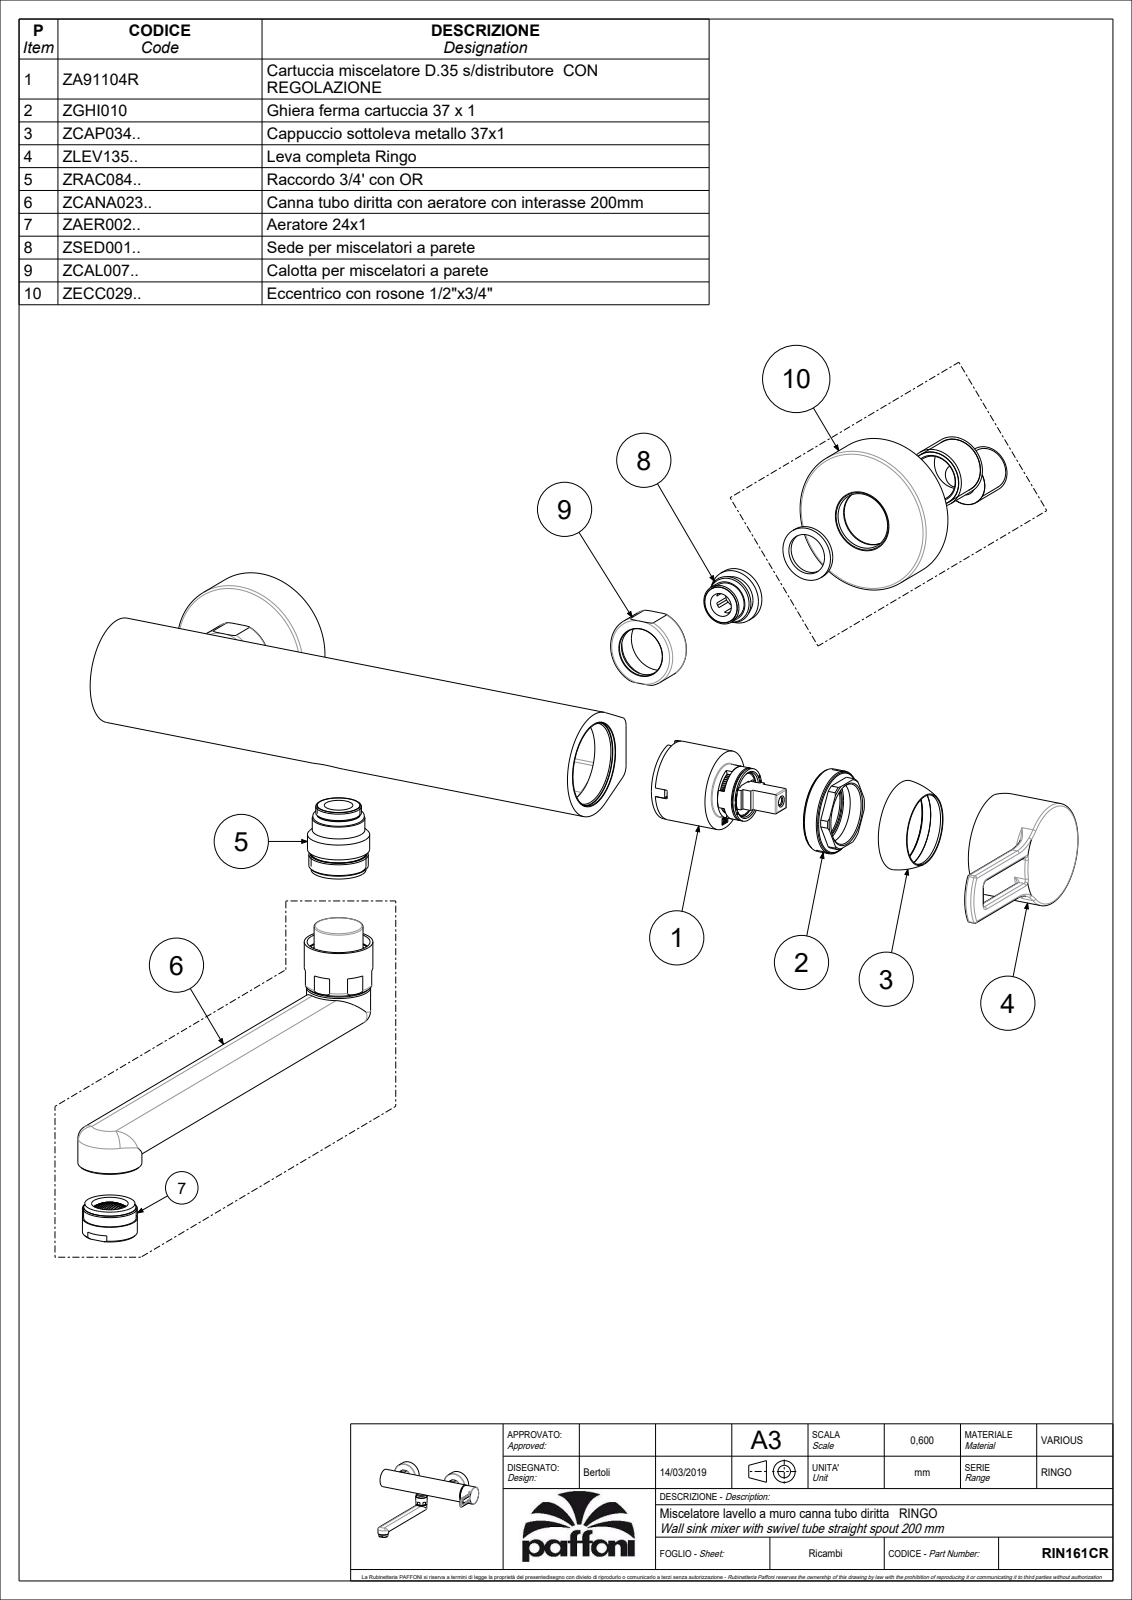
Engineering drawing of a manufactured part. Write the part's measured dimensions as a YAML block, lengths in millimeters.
part_name: "RIN161CR"
step_written_by: "CREO PARAMETRIC BY PTC INC, 2020044 (CONFIG_CONTROL_DESIGN)"
units: millimeters
bodies: {solids: 4, faces: 3079, planar: 2184, cylindrical: 470, other: 425}
overall_size: [277, 273, 110.3]
volume: 296195
surface_area: 205163
round_holes:
  - {diameter: 20, count: 4}
  - {diameter: 7, count: 3}
  - {diameter: 10.5, count: 3}
  - {diameter: 4, count: 2}
  - {diameter: 9.5, count: 2}
  - {diameter: 16, count: 2}
  - {diameter: 18, count: 2}
  - {diameter: 21.6, count: 2}
  - {diameter: 26, count: 2}
  - {diameter: 62.3, count: 2}
  - {diameter: 2.5, count: 1}
  - {diameter: 3, count: 1}
round_bosses_or_shafts:
  - {diameter: 28, count: 3}
  - {diameter: 63.5, count: 2}
  - {diameter: 27, count: 2}
  - {diameter: 26.2, count: 2}
  - {diameter: 24, count: 2}
  - {diameter: 23, count: 2}
  - {diameter: 20.5, count: 2}
  - {diameter: 19.5, count: 2}
partial_cylinders:
  - {radius: 1.5, count: 44}
  - {radius: 0.5, count: 34}
  - {radius: 1, count: 14}
  - {radius: 0.15, count: 11}
  - {radius: 0.3, count: 4}
  - {radius: 1.3, count: 4}
  - {radius: 6, count: 4}
  - {radius: 7, count: 3}
face_to_face_distances: [15, 3.7, 1, 0.6, 29.8, 3.5, 29.2, 14.2, 26.3, 10.7]
hole_center_spacings: [7.07, 8.6, 11.4, 150, 4, 6, 10, 11]
